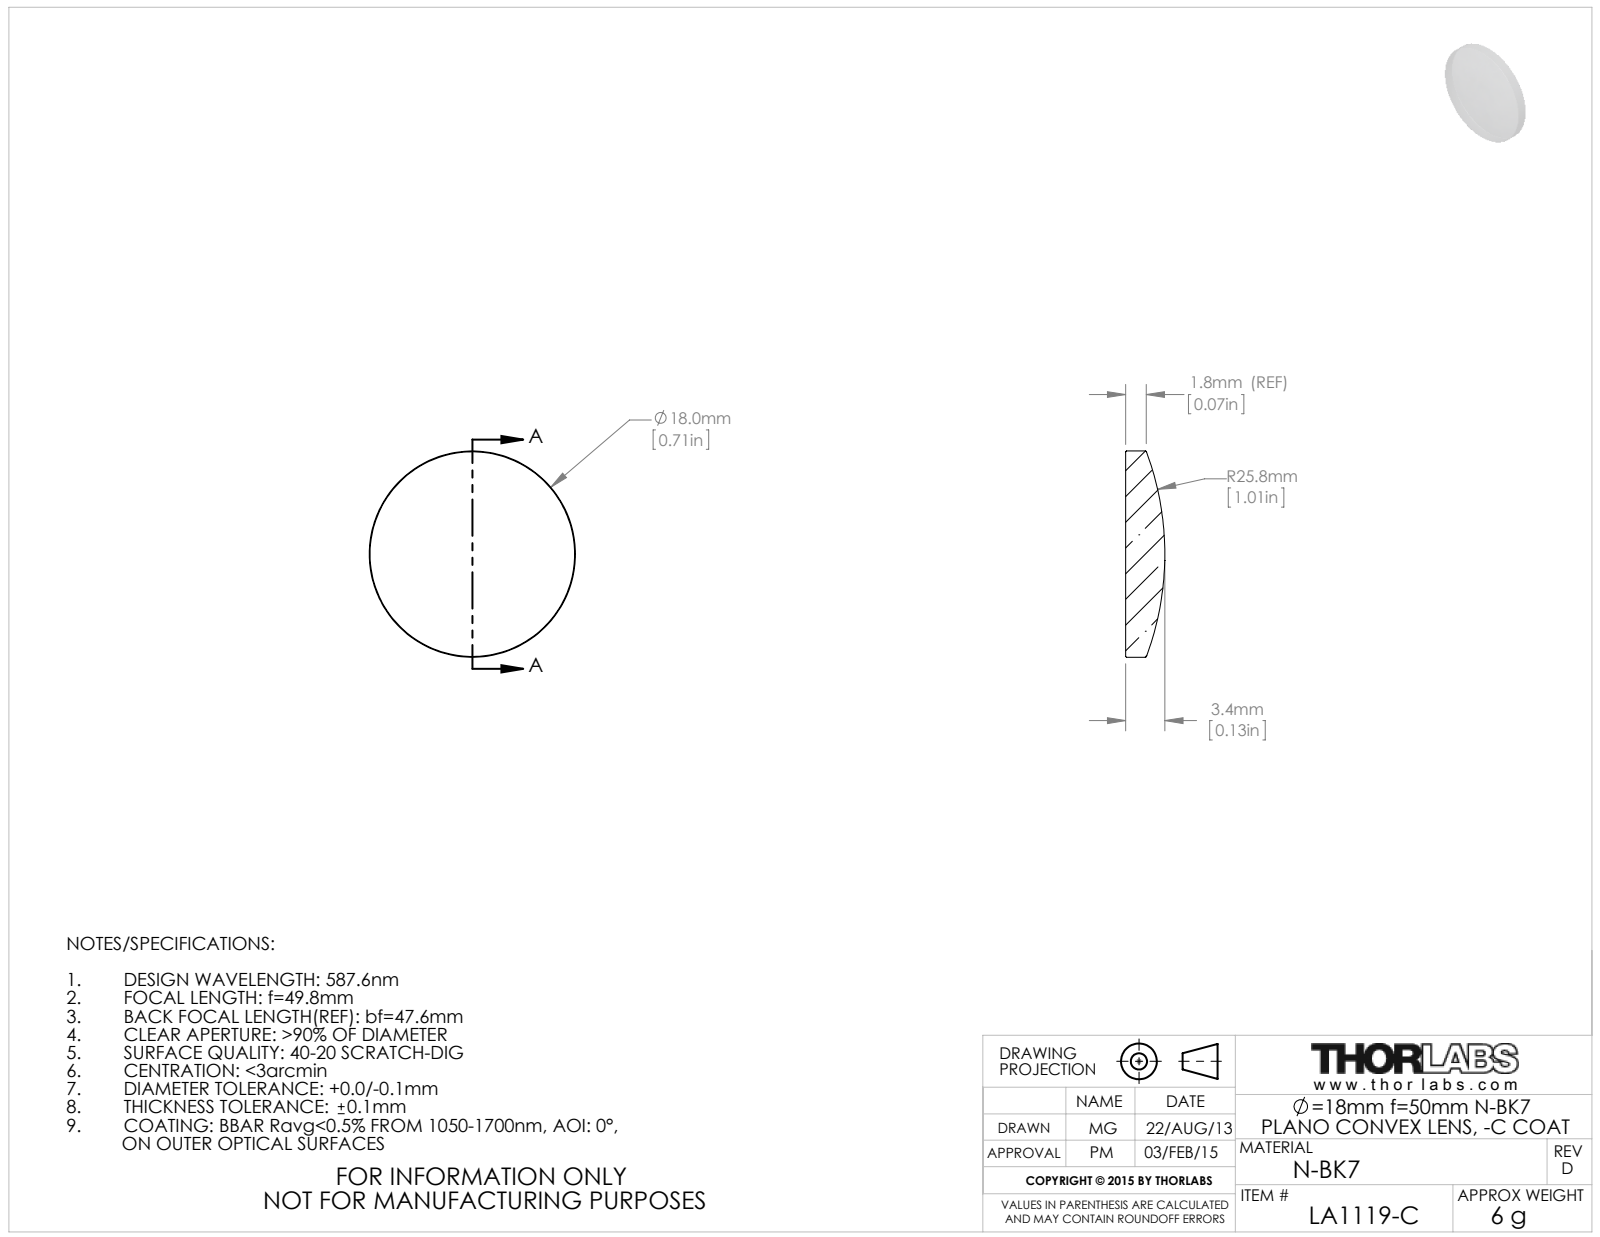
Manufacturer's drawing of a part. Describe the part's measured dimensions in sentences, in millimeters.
The part is named "4576-E0W". Its 3-D file was written by "SolidWorks 2009 (AUTOMOTIVE_DESIGN)". It is 1 solid with 5 faces: 1 planar, 2 cylindrical and 2 other. Overall it measures 18 by 18 by 3.42 millimeters. Its volume is 666 cubic millimeters and its surface area 619 square millimeters. Round bosses or shafts: 1 of diameter 18.
